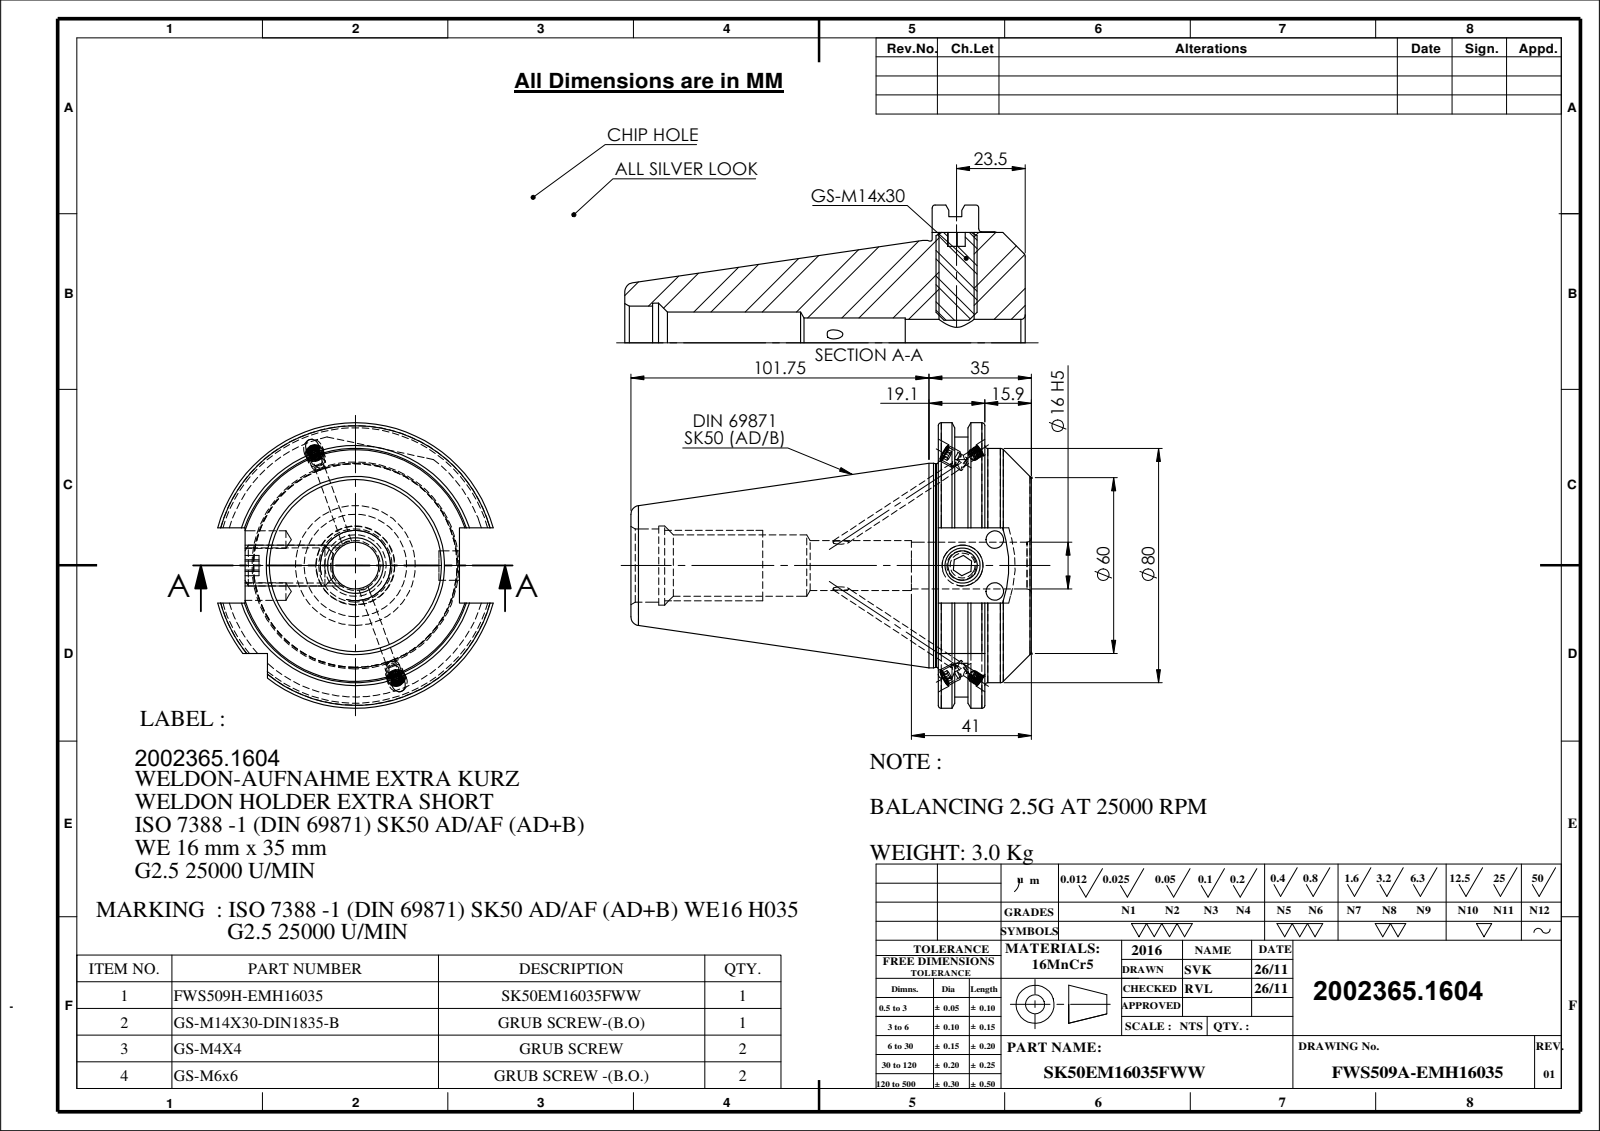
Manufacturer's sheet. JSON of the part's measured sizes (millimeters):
{"part_name": "M6X6_DIN 913 - M6 x 6-N; GS-M4X4_DIN 913 - M4 x 4-N; 91506-WE716035; SK50EM16035FWW (+1 more)", "step_written_by": "SolidWorks 2018 (CONFIG_CONTROL_DESIGN)", "units": "millimeters", "bodies": {"solids": 6, "faces": 274, "planar": 74, "cylindrical": 83, "other": 117}, "overall_size": [136.75, 97.5, 94.05], "volume_mm3": 389688, "surface_area_mm2": 51524, "round_holes": [[3.3, 2], [4.5, 2], [5, 2], [6, 2], [6.5, 2], [10, 1], [12, 1], [16, 1], [17, 1], [21, 1], [25, 1], [27, 1]], "round_bosses_or_shafts": [[6, 2], [4, 2], [69.85, 1], [69.45, 1], [14, 1]], "partial_cylinders_radius": [[40, 1], [44.9, 1], [48.75, 1]], "face_to_face_distances": [15.9, 31.8, 5.66, 10.24, 26.14, 10.14, 4.48, 5.76, 21.66, 73.2], "hole_center_spacings": [14.12, 14.39, 0.35, 17.7]}
